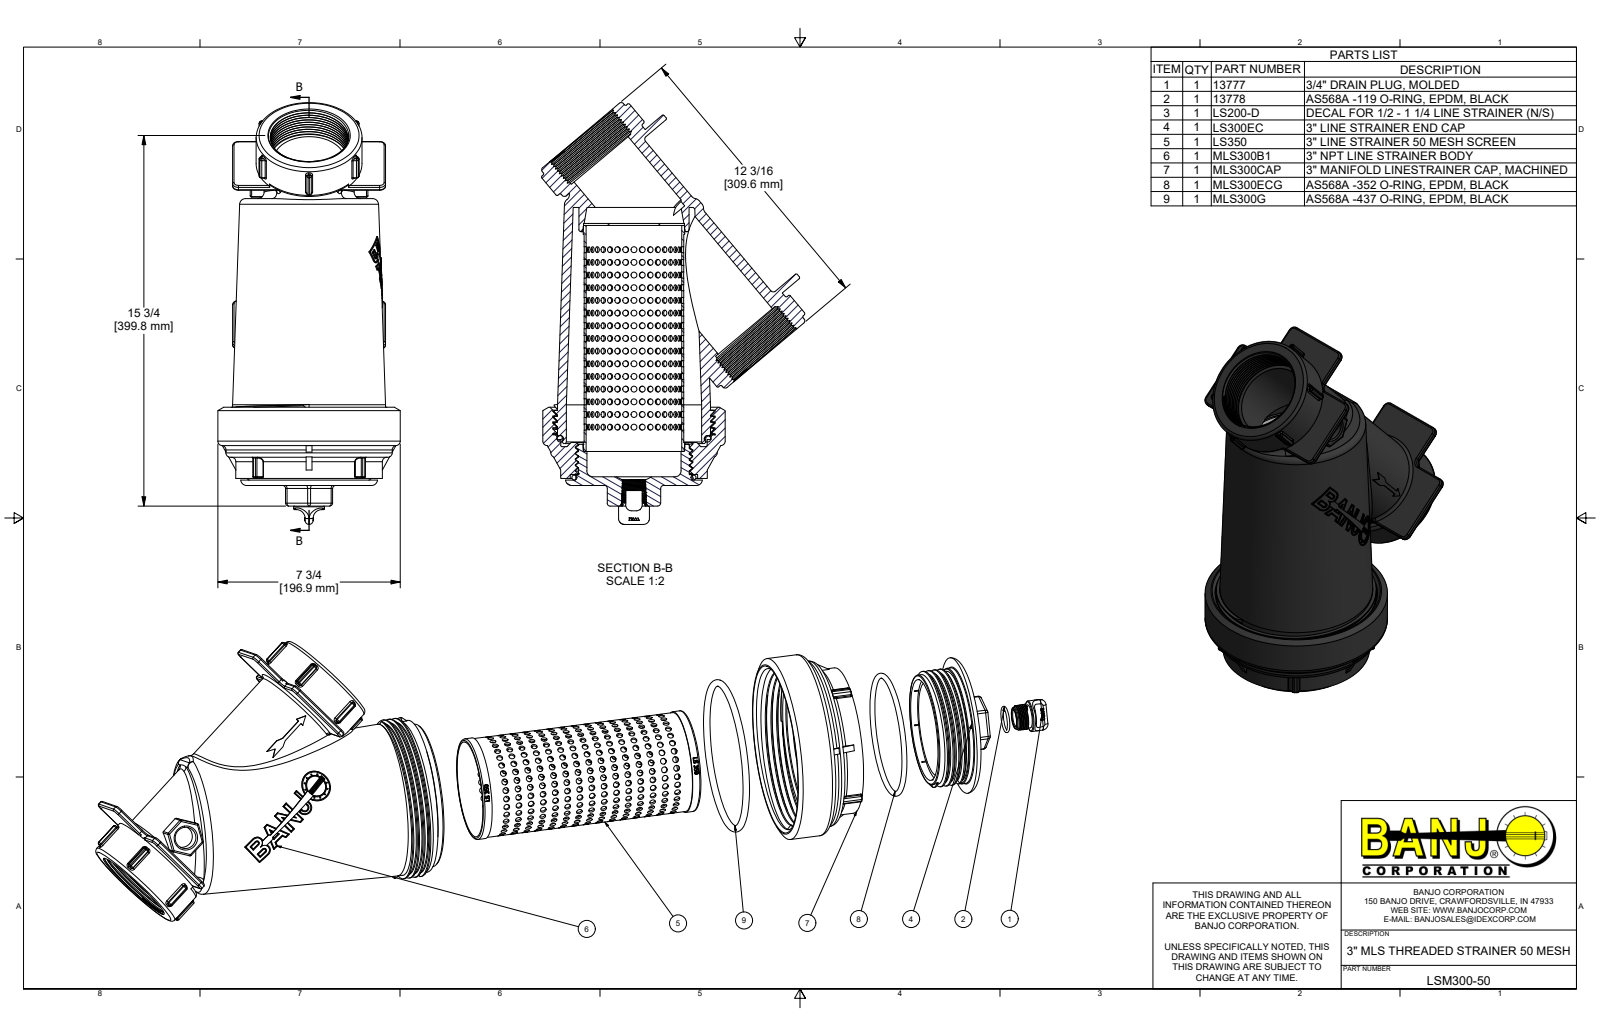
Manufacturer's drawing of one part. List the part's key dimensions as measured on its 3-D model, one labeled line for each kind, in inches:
Part name (STEP PRODUCT): LSM300-50; MLS300B1; 13777; 13778 (+7 more)
STEP written by: Autodesk Inventor 2022 (AUTOMOTIVE_DESIGN)
Units: inches
Bodies: 8 solids, 2120 faces (570 planar, 960 cylindrical, 590 other)
Overall size (bounding box): 17.915 × 11.198 × 7.75
Volume: 197.9 in³ · Surface area: 1 289 in²
Round holes (diameter × count): ⌀0.25 ×450, ⌀3.3 ×2, ⌀0.7 ×1, ⌀0.817 ×1, ⌀0.91 ×1, ⌀1.154 ×1, ⌀3 ×1, ⌀4 ×1, ⌀4.063 ×1, ⌀4.317 ×1, ⌀4.32 ×1, ⌀4.729 ×1
Round bosses / shafts (diameter × count): ⌀4.5 ×2, ⌀7.75 ×1, ⌀7.07 ×1, ⌀6.8 ×1, ⌀6.5 ×1, ⌀6.23 ×1, ⌀6.1 ×1, ⌀4.955 ×1
Partial cylindrical surfaces — rounded edges, fillets, slot ends (radius × count): R0.06 ×129, R0.09 ×32, R0.03 ×24, R0.25 ×19, R0.125 ×18, R0.02 ×8, R0.015 ×6, R0.071 ×2
Main face-to-face distances: 8.564, 0.3, 0.251, 8.815, 0.23, 10.627, 1.562, 0.37, 0.07, 11.809
Hole centre spacings: 1.077, 1.615, 2.692, 0.538, 3.769, 2.154, 0.539, 3.23
